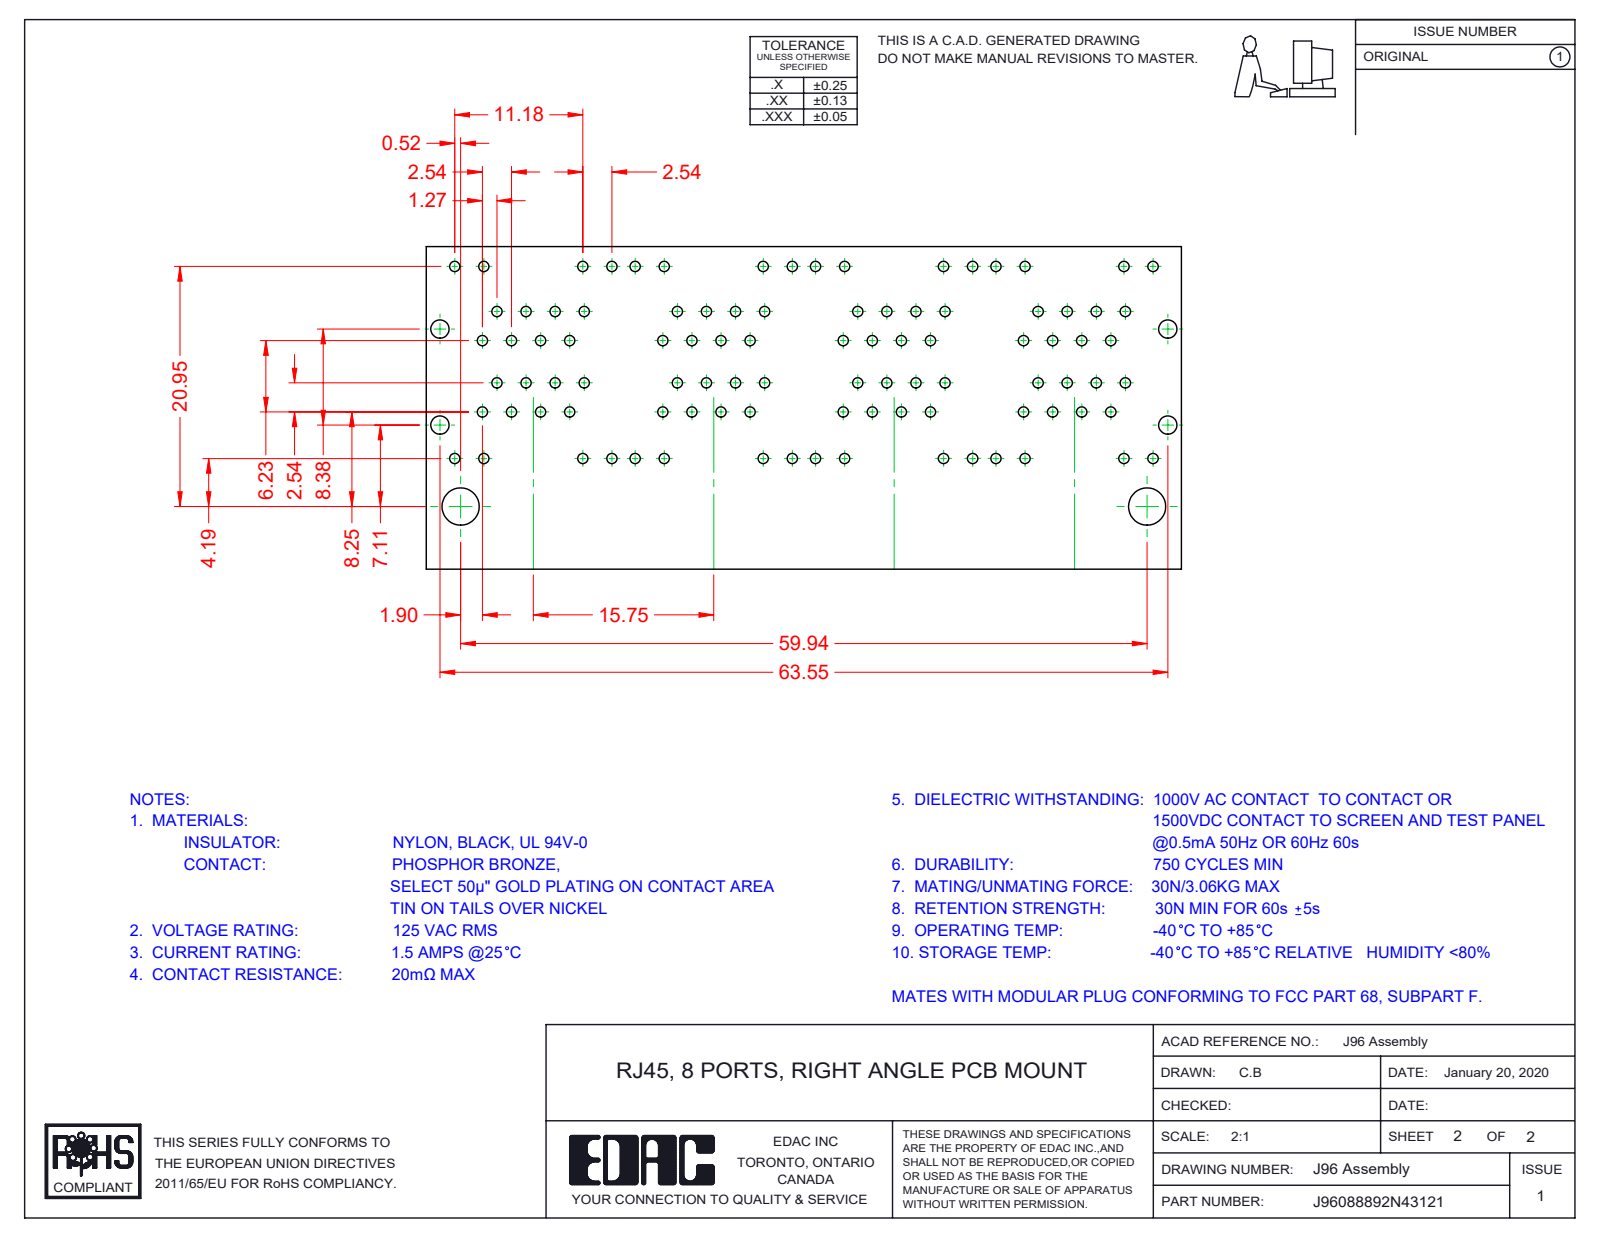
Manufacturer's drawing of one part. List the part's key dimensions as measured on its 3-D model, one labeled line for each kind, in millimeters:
Part name (STEP PRODUCT): 96 Grounding_8 Ports; 96 LED LH Upper_4-Orange; 96 Insulator_8 Ports; 96 Insulator Insert (+8 more)
STEP written by: SolidWorks 2016 (CONFIG_CONTROL_DESIGN)
Units: millimetres
Bodies: 96 solids, 7642 faces (6069 planar, 1307 cylindrical, 266 other)
Overall size (bounding box): 64.05 × 29.58 × 28.68
Volume: 24 160 mm³ · Surface area: 63 658 mm²
Round holes (diameter × count): ⌀1.7 ×3
Round bosses / shafts (diameter × count): ⌀1.68 ×3
Partial cylindrical surfaces — rounded edges, fillets, slot ends (radius × count): R0.25 ×124, R0.35 ×73, R1 ×72, R0.5 ×49, R0.91 ×32, R0.2 ×21, R0.7 ×11, R0.22 ×8
Main face-to-face distances: 15.75, 0.35, 9.95, 1.17, 1.6, 0.54, 9.98, 10.18, 12.67, 3.37
Hole centre spacings: 15.75, 31.5
